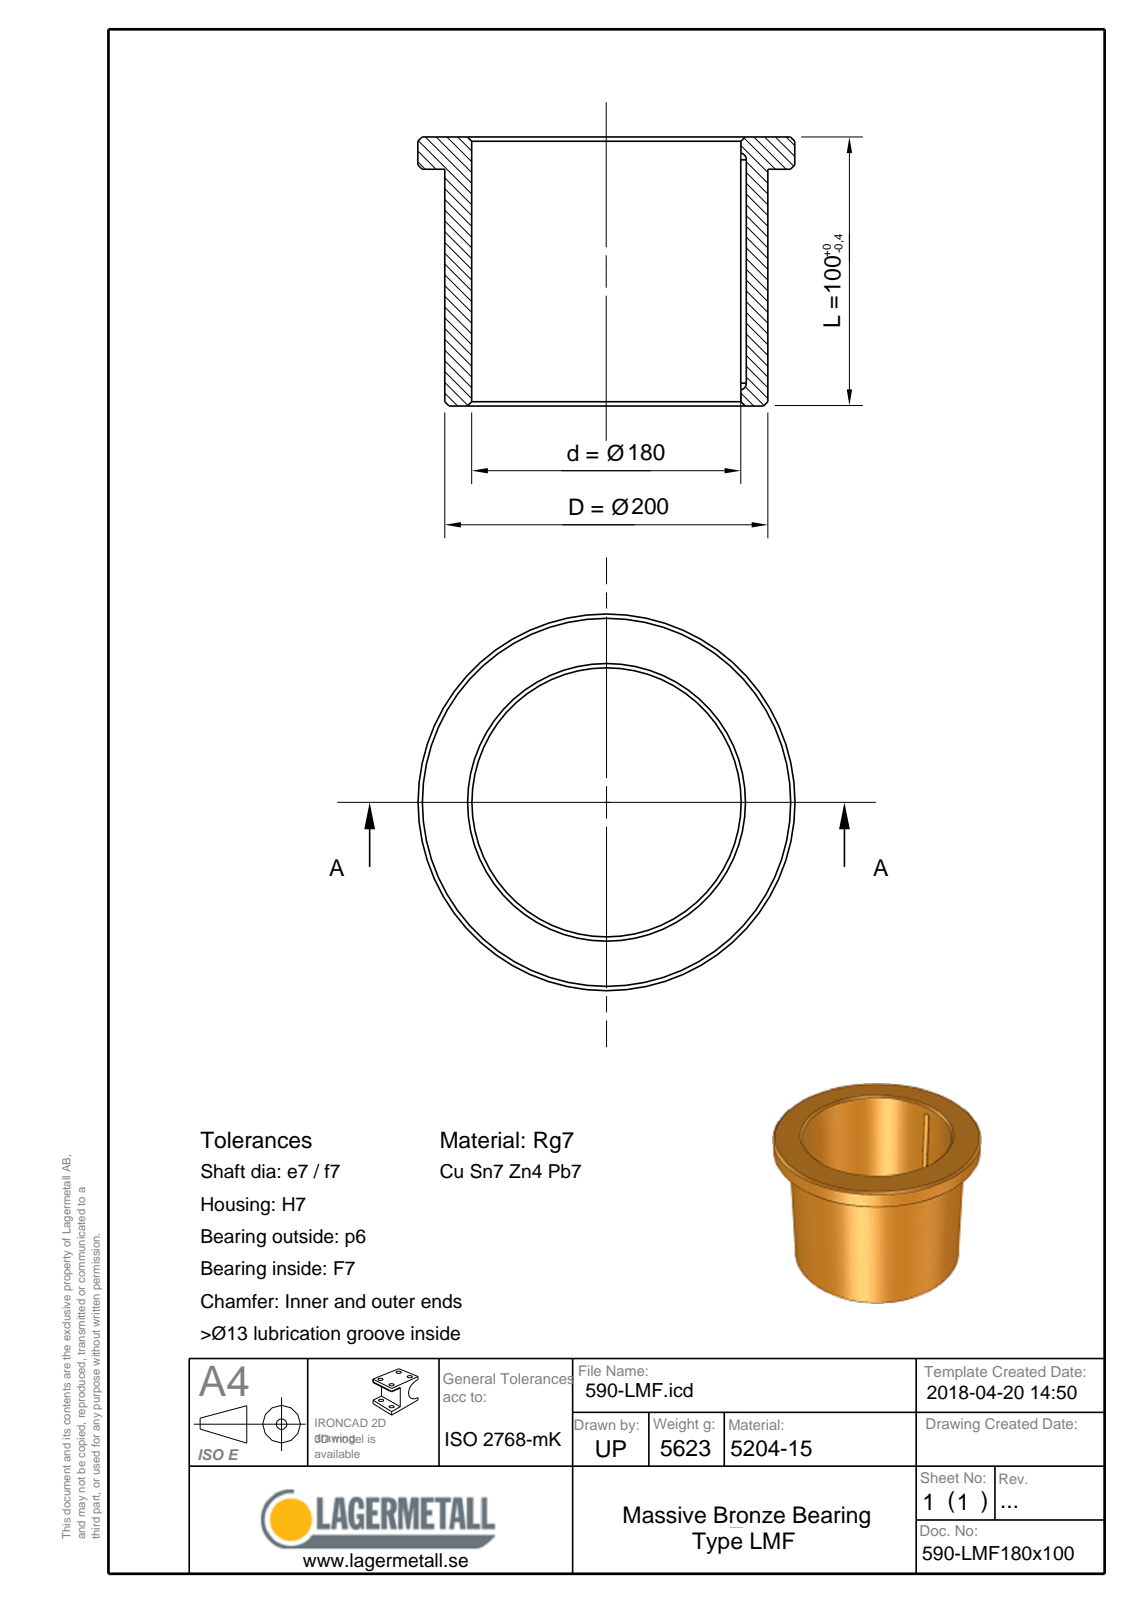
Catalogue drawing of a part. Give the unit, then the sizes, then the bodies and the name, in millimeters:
Units: millimetres
Overall size (bounding box): 215 × 215 × 100
Round holes (diameter × count): ⌀180 ×1
Round bosses / shafts (diameter × count): ⌀215 ×1, ⌀200 ×1
Partial cylindrical surfaces — rounded edges, fillets, slot ends (radius × count): R2.25 ×2
Main face-to-face distances: 100, 90, 10
Volume: 638 970 mm³ · Surface area: 138 115 mm²
Bodies: 1 solid, 16 faces (4 planar, 5 cylindrical, 7 other)
Part name (STEP PRODUCT): 590-LMF180x100
STEP written by: Spatial InterOp 3D (CONFIG_CONTROL_DESIGN)
